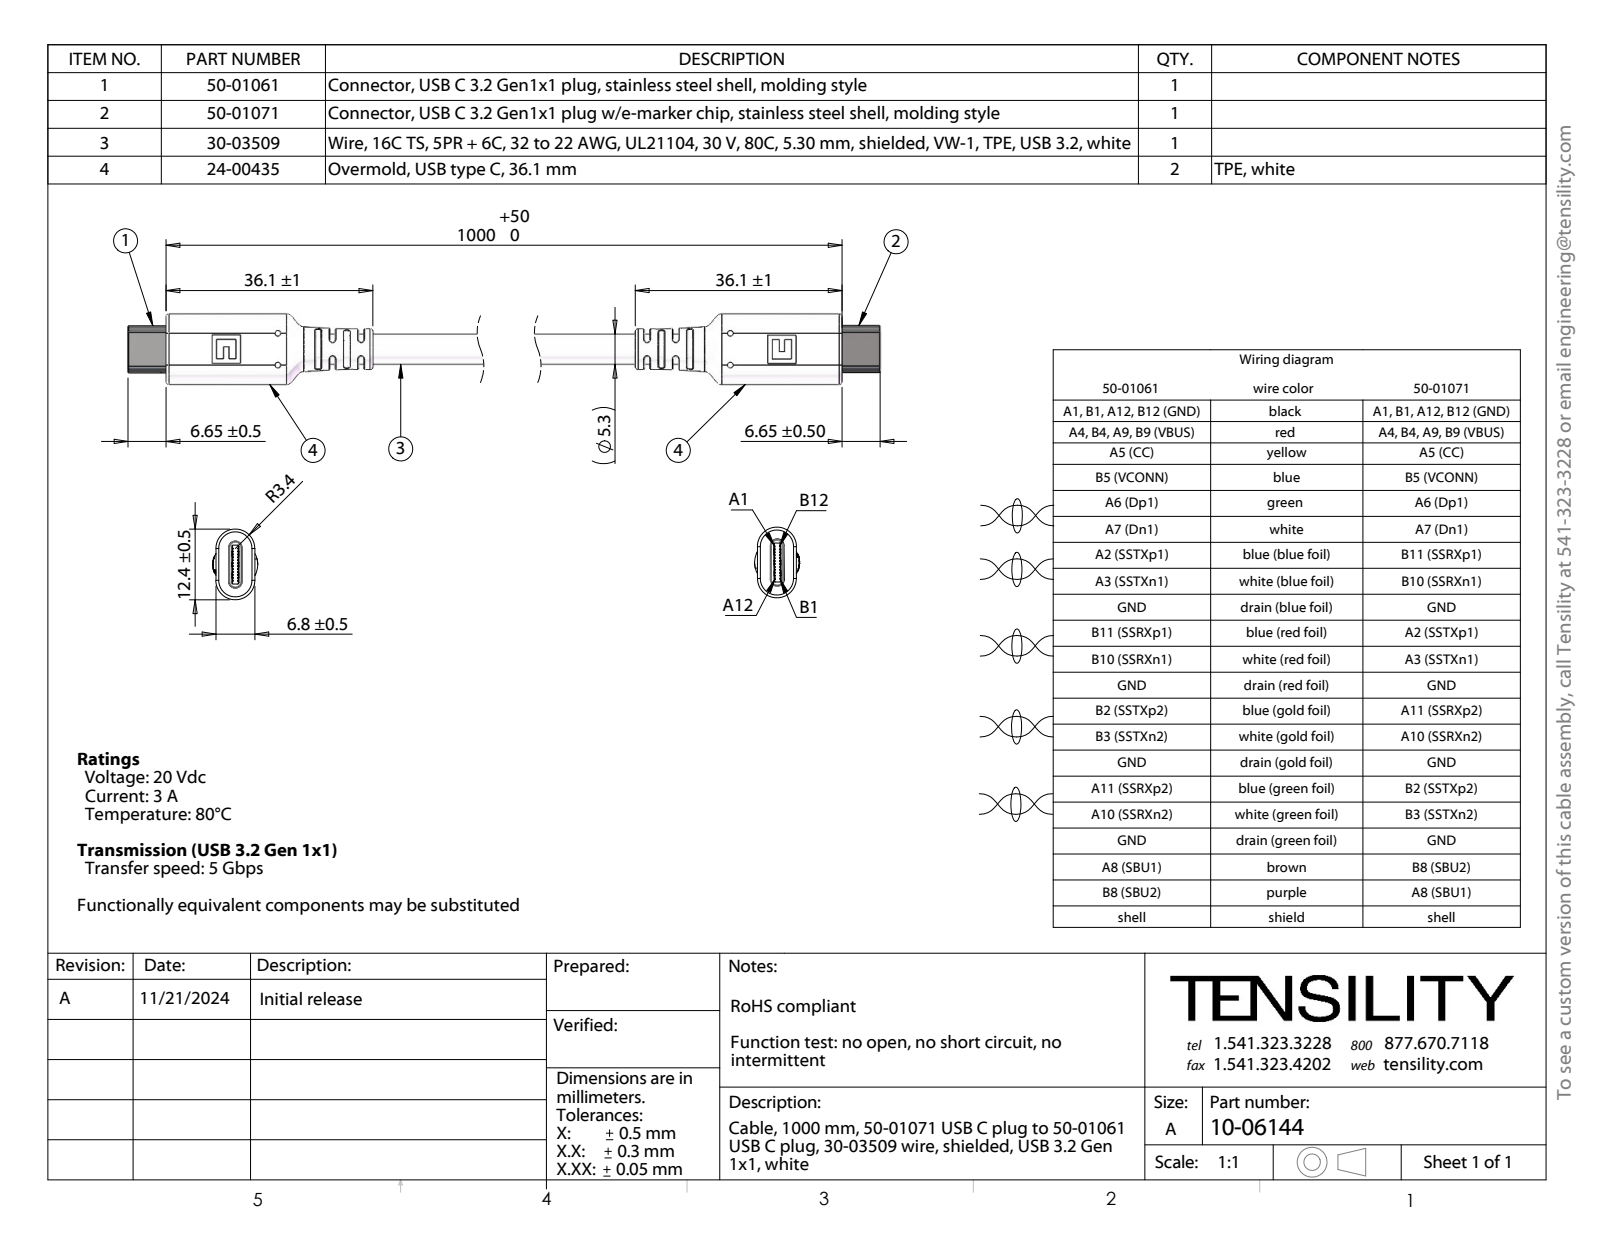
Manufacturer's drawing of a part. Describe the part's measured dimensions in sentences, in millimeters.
The part is named "10-06144; 30-03509; 50-01061_Hidden emarker; 50-01071_Hidden emarker (+1 more)". Its 3-D file was written by "SolidWorks 2021 (CONFIG_CONTROL_DESIGN)". It is 168 solids with 1726 faces: 728 planar, 766 cylindrical and 232 other. Overall it measures 215.4 by 12.35 by 7.89 millimeters. Its volume is 6 767 cubic millimeters and its surface area 49 412 square millimeters. Round holes: 4 of diameter 1, 1 of diameter 4.16, 1 of diameter 4.17, 1 of diameter 4.19, 1 of diameter 4.2, 1 of diameter 4.4. Round bosses or shafts: 8 of diameter 0.74, 4 of diameter 0.48, 4 of diameter 0.25, 2 of diameter 0.55, 1 of diameter 7.82, 1 of diameter 5.3, 1 of diameter 1, 1 of diameter 0.9. Partial cylindrical surfaces (rounded edges, fillets, slot ends): 20 of radius 0.5, 8 of radius 0.25, 4 of radius 0.1, 4 of radius 0.15, 4 of radius 1.18, 2 of radius 0.3, 2 of radius 0.31, 2 of radius 0.47. The main face-to-face distances are 1.03, 1.02, 0.95, 1.1, 1.04, 6.8, 0.62, 2.5, 1, 2.35. The hole center spacings are 0.64, 2.06, 1.64, 0.59, 2.08, 2.11, 0.62, 2.
